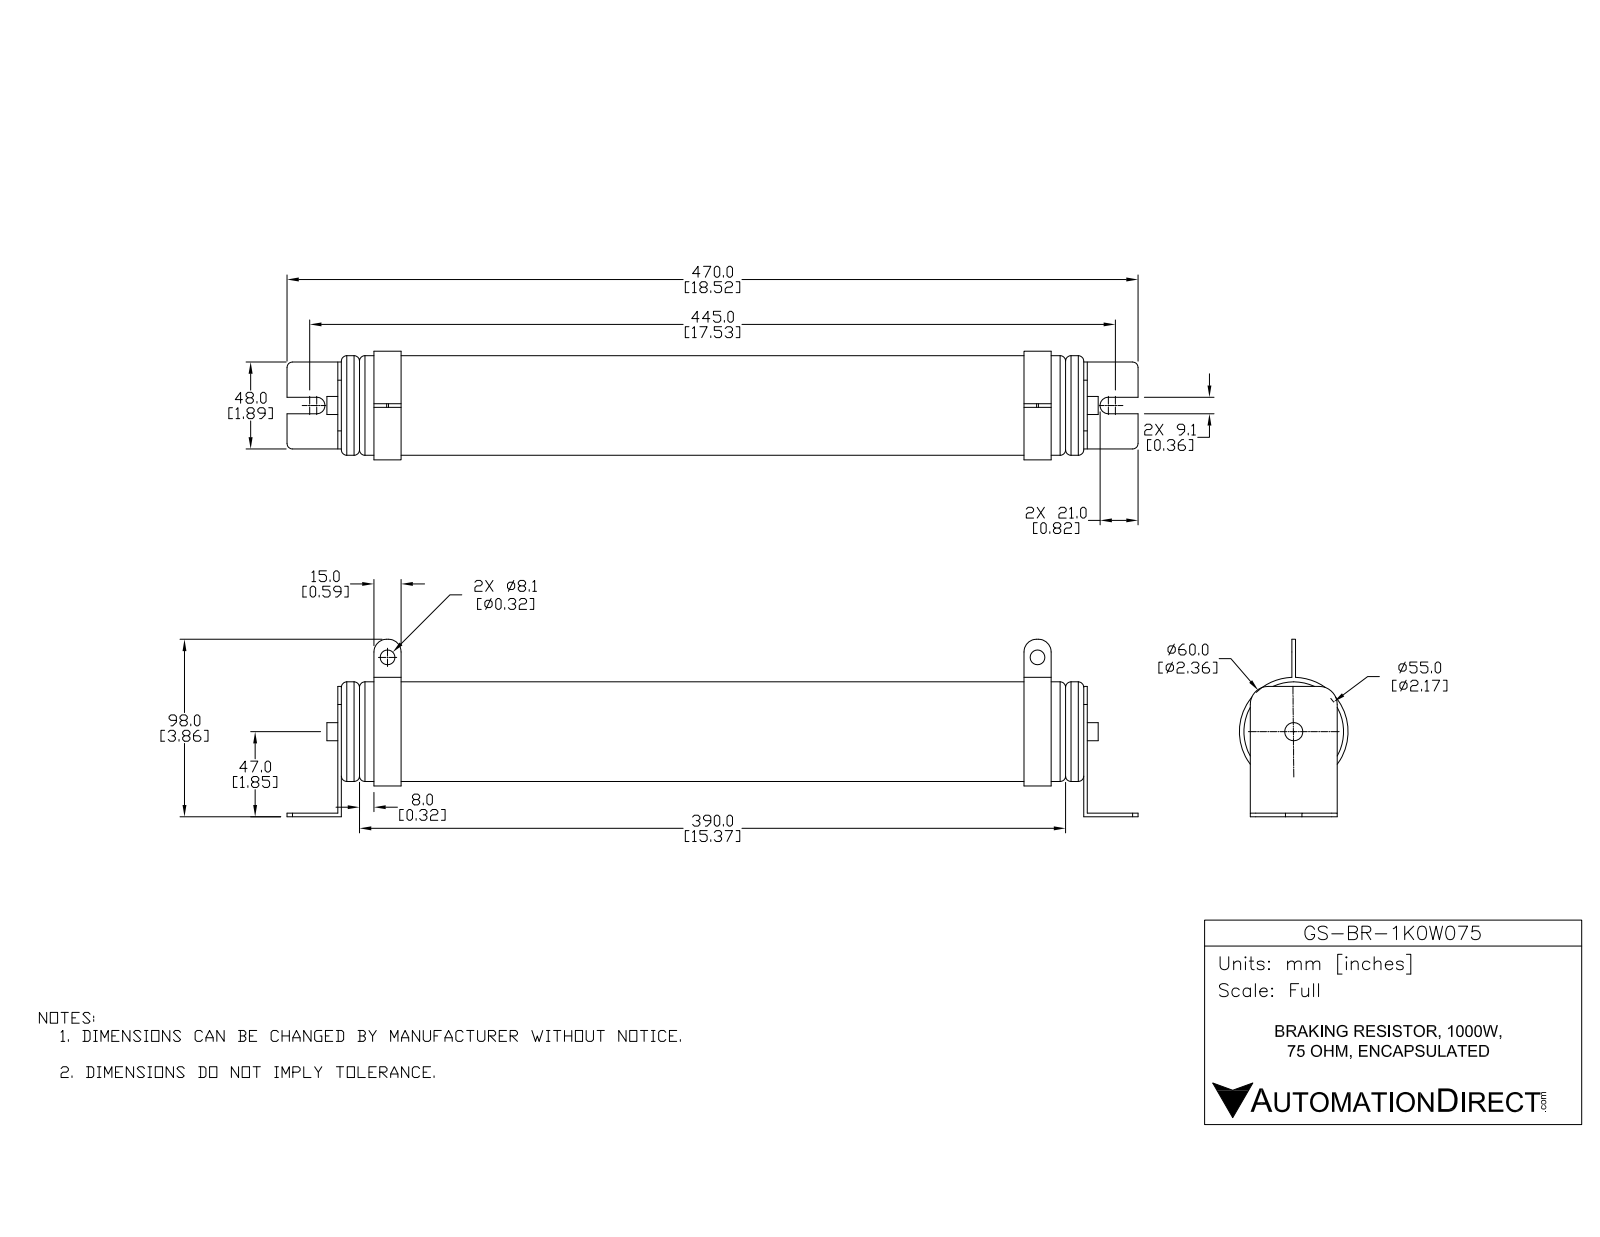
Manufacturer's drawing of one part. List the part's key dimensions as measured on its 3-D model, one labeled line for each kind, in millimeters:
Part name (STEP PRODUCT): GS-BR-1K0W075
STEP written by: SolidWorks 2015 (AUTOMOTIVE_DESIGN)
Units: millimetres
Bodies: 2 solids, 91 faces (41 planar, 38 cylindrical, 12 other)
Overall size (bounding box): 470 × 98 × 60
Volume: 1 006 000 mm³ · Surface area: 92 390 mm²
Round holes (diameter × count): ⌀8.1 ×2
Round bosses / shafts (diameter × count): ⌀60 ×1, ⌀55 ×1, ⌀55 ×1, ⌀10 ×1
Partial cylindrical surfaces — rounded edges, fillets, slot ends (radius × count): R3 ×4, R7 ×4, R4.5 ×2, R10 ×2
Main face-to-face distances: 2, 414, 412, 410, 35, 379, 33, 377, 20, 394
Hole centre spacings: 359
